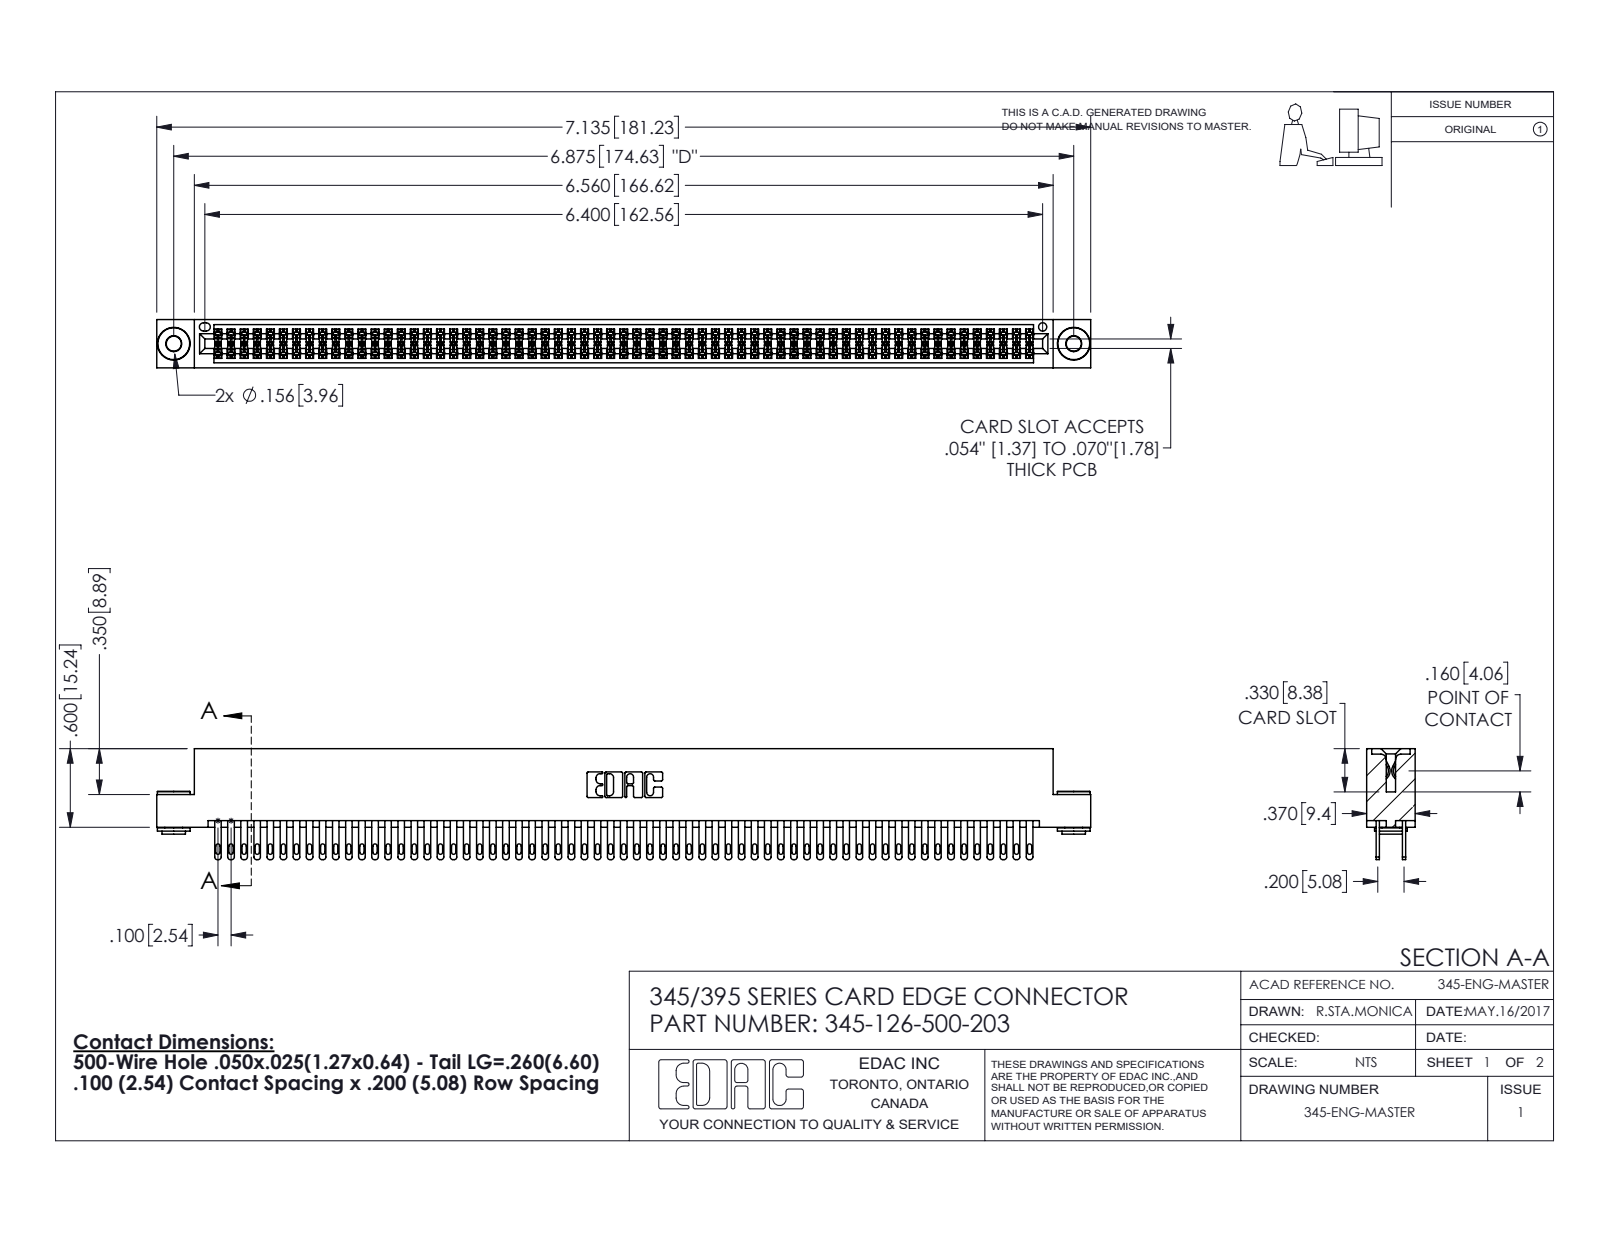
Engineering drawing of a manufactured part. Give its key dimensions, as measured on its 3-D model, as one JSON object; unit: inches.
{"part_name": "345-126-500-203; 345-250-002_345-250-002-102; 345-292-001_345-293-100; 345 Part_Flush Mounting Lugs - 0.156 Dia-TH", "step_written_by": "SolidWorks 2016 (CONFIG_CONTROL_DESIGN)", "units": "inches", "bodies": {"solids": 129, "faces": 5960, "planar": 3492, "cylindrical": 2460, "other": 8}, "overall_size": [7.135, 0.847, 0.37], "volume_in3": 1.111, "surface_area_in2": 44.65, "round_holes": [[0.116, 2], [0.156, 2], [0.064, 1]], "round_bosses_or_shafts": [[0.25, 2], [0.18, 2], [0.136, 2]], "partial_cylinders_radius": [[0.006, 189], [0.016, 126], [0.02, 126], [0.01, 22], [0.007, 6], [0.031, 6], [0.026, 3], [0.014, 2]], "face_to_face_distances": [0.072, 0.298, 0.2, 0.025, 0.098, 0.272, 0.37, 0.225, 0.175, 0.149], "hole_center_spacings": [0.27, 6.639, 6.875]}
